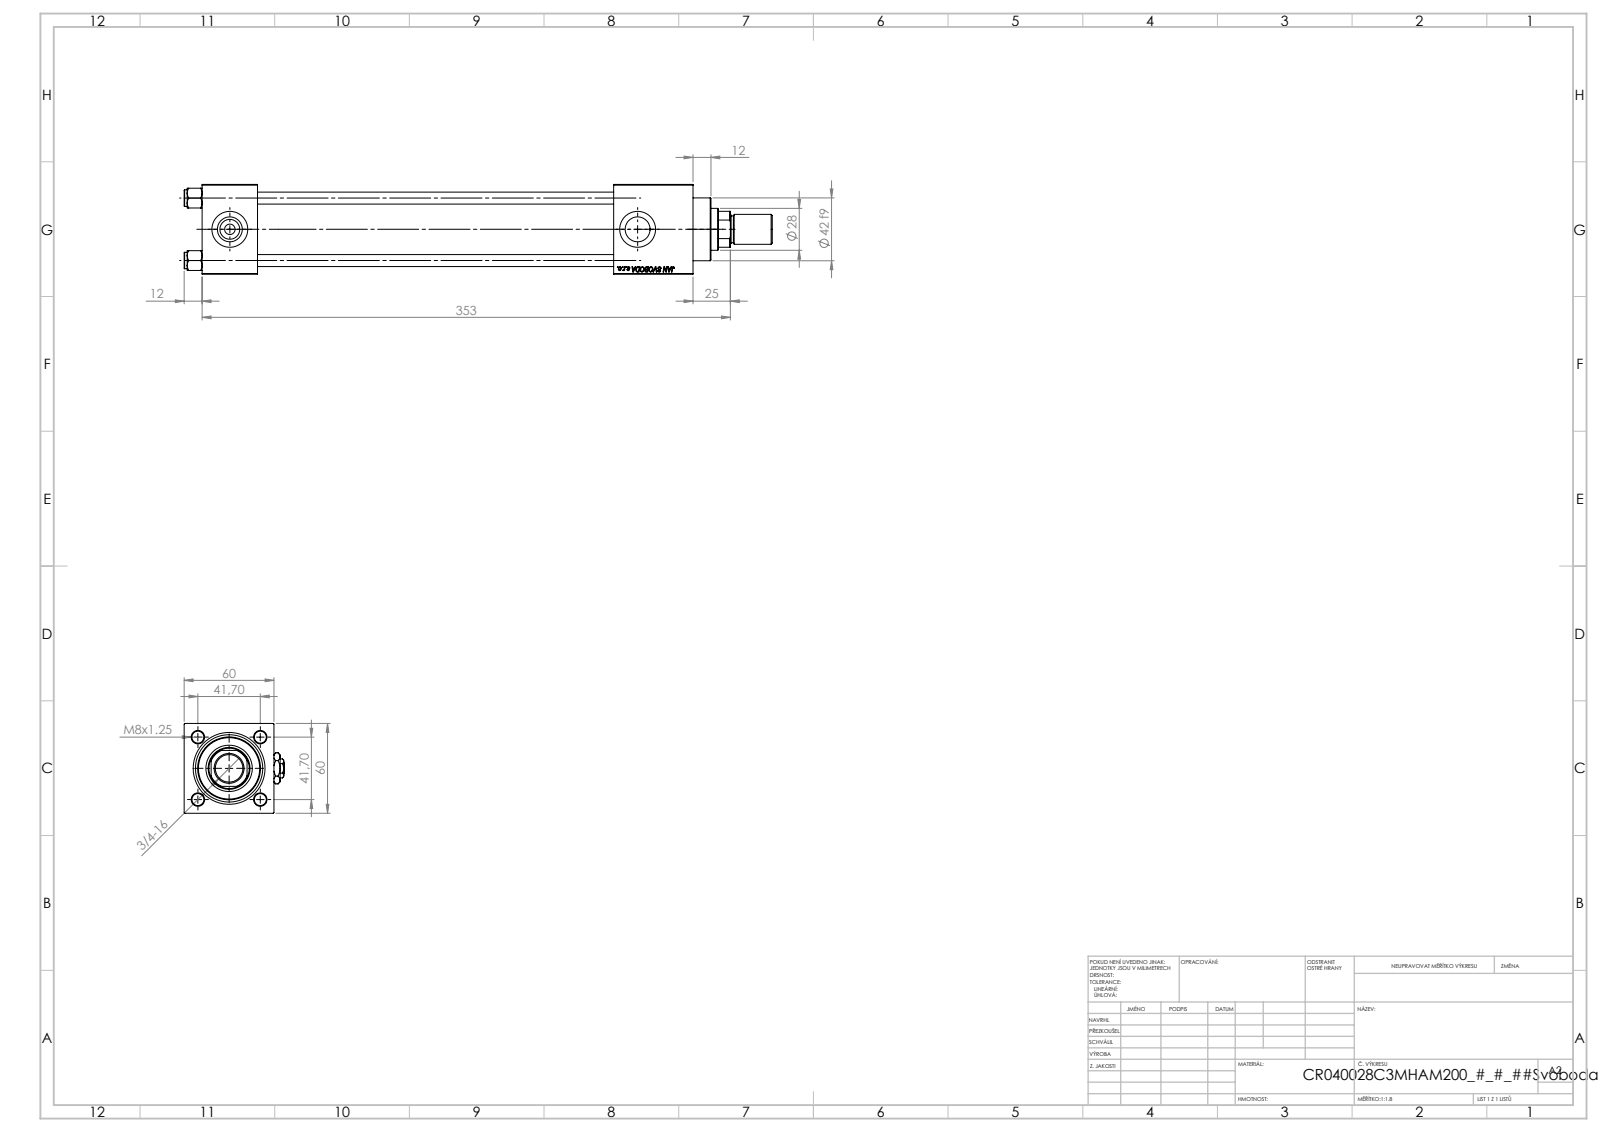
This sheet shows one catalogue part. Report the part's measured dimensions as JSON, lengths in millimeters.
{"part_name": "NUT_M5_C; V215CR_C_Body; V215_VC_A; Zatka_pro_OIL_PORT (+3 more)", "step_written_by": "SolidWorks 2019 (CONFIG_CONTROL_DESIGN)", "units": "millimeters", "bodies": {"solids": 14, "faces": 1264, "planar": 578, "cylindrical": 102, "other": 584}, "overall_size": [393, 67, 60], "volume_mm3": 649564, "surface_area_mm2": 199345, "round_holes": [[8, 4], [7, 2], [16.66, 2], [24, 2], [18.5, 1], [28, 1], [31, 1], [40, 1], [45, 1]], "round_bosses_or_shafts": [[11, 4], [46, 1], [42, 1], [20, 1], [18, 1]], "partial_cylinders_radius": [[13.5, 1]], "face_to_face_distances": [60, 37, 275, 238, 53, 299.3, 262.3, 24.3, 328, 291], "hole_center_spacings": [29.49, 41.7, 58.97, 272.5]}
